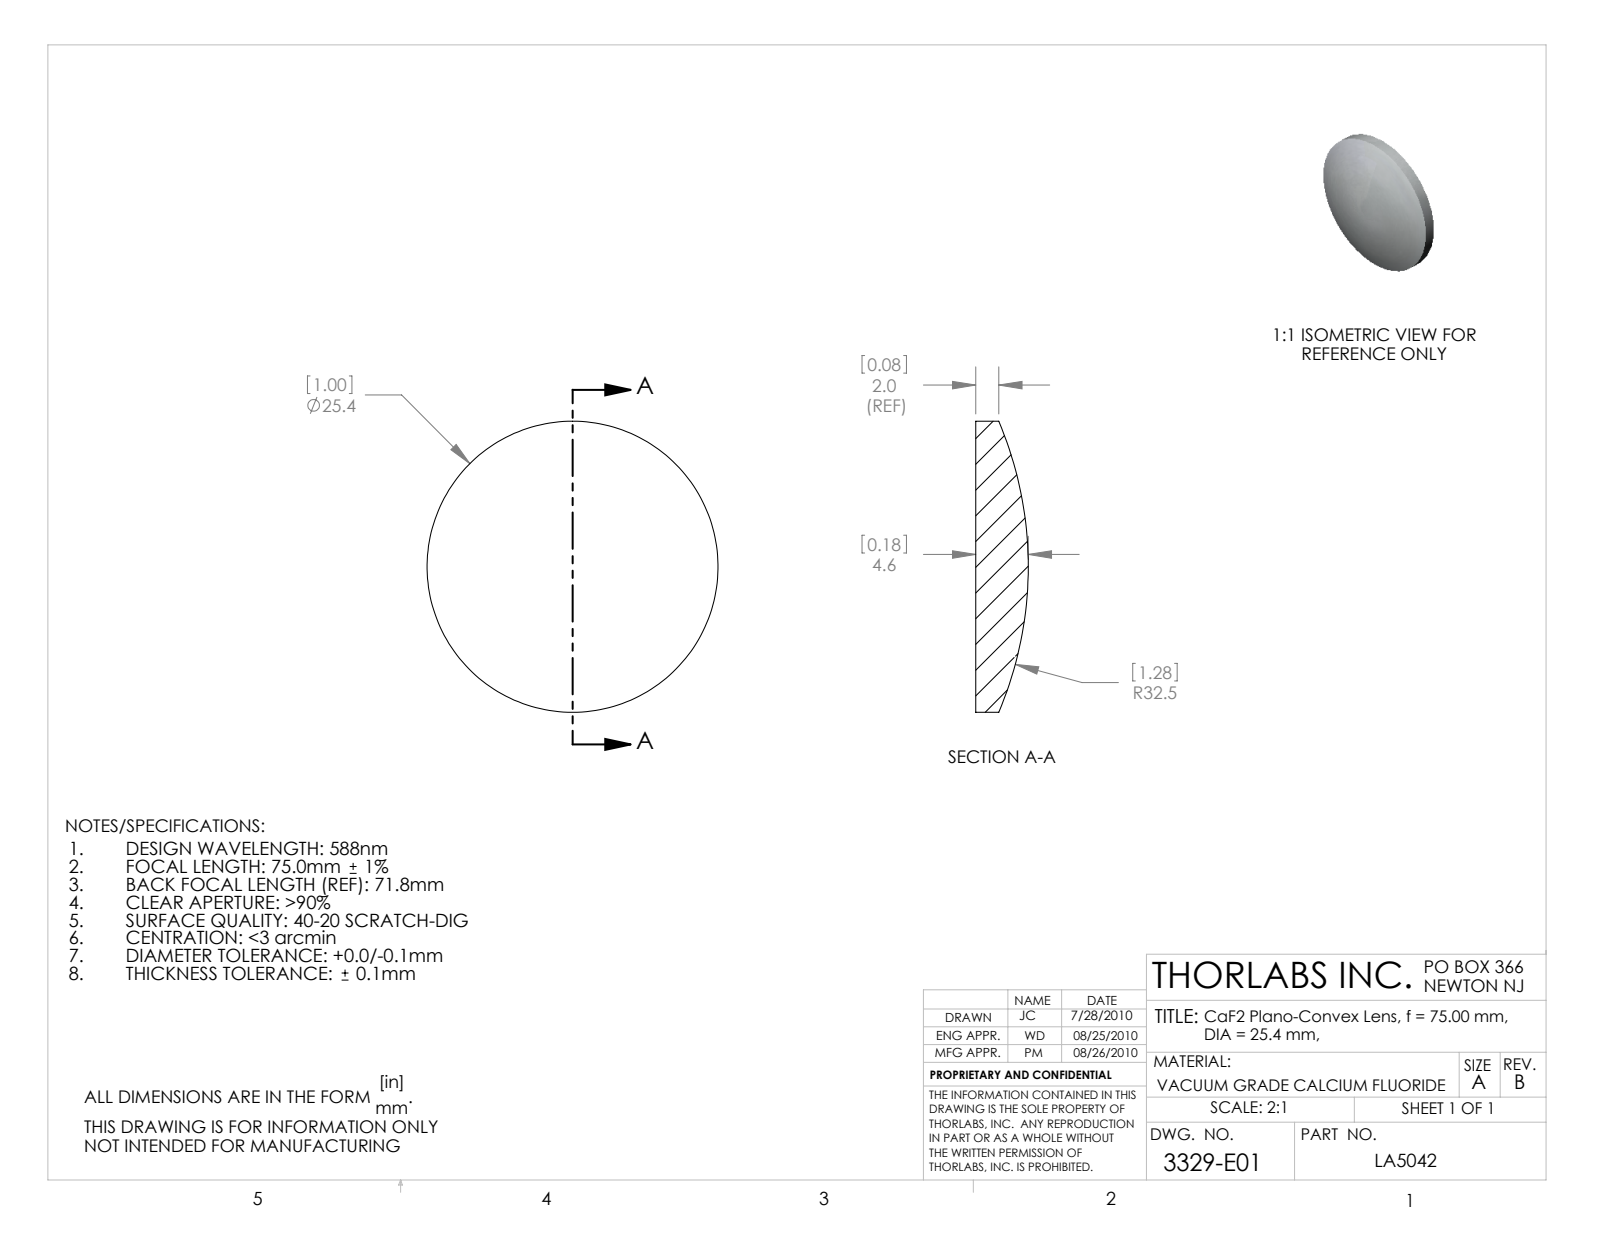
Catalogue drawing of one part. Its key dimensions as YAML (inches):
part_name: "3329-E0W"
step_written_by: "SolidWorks 2009 (AUTOMOTIVE_DESIGN)"
units: inches
bodies: {solids: 1, faces: 5, planar: 1, cylindrical: 2, other: 2}
overall_size: [1, 1, 0.18]
volume: 0.102
surface_area: 1.851
round_bosses_or_shafts:
  - {diameter: 1, count: 1}
